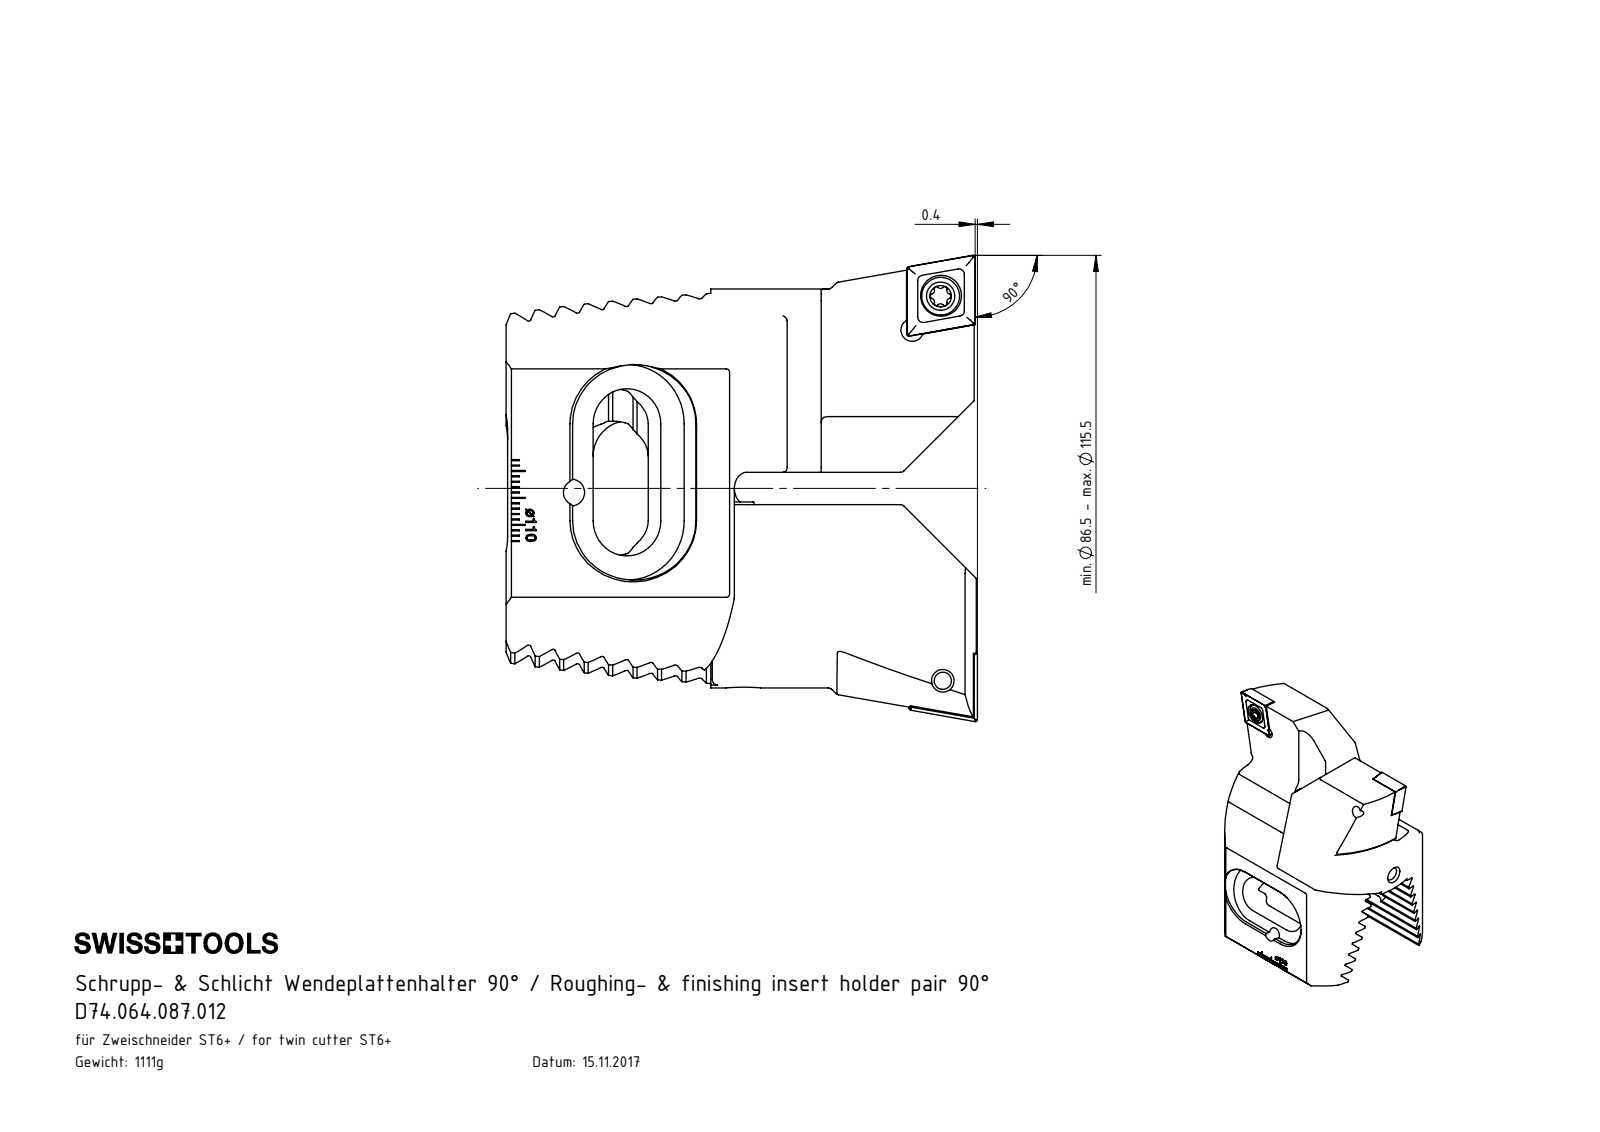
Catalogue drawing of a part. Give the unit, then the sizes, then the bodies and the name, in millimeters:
Units: millimetres
Overall size (bounding box): 87.5 × 86.5 × 58.2
Round holes (diameter × count): ⌀4.2 ×4, ⌀5 ×2, ⌀5.5 ×2, ⌀7.6 ×2, ⌀2 ×1, ⌀2.5 ×1, ⌀8 ×1
Round bosses / shafts (diameter × count): ⌀7 ×2, ⌀5 ×2, ⌀6 ×1, ⌀4 ×1, ⌀3 ×1, ⌀2 ×1
Partial cylindrical surfaces — rounded edges, fillets, slot ends (radius × count): R0.34 ×16, R1 ×16, R0.39 ×12, R0.69 ×6, R0.69 ×6, R3 ×4, R6.5 ×4, R11 ×4
Main face-to-face distances: 4.07, 8.14, 20.36, 12.21, 28.8, 29.4, 58.2, 16.29, 20.34, 24.43
Hole centre spacings: 8.21, 8.33, 71.43, 20, 58.76, 65.23, 65.3, 65.33
Volume: 142 276 mm³ · Surface area: 37 228 mm²
Bodies: 8 solids, 746 faces (411 planar, 143 cylindrical, 192 other)
Part name (STEP PRODUCT): ISO 4028 - M3 x 5_M3x8; Z72-ER3.001.030; ZC7-xxx.001.050_A; ZC7-xxx.001.050_A_versetzt Combi (+3 more)
STEP written by: SolidWorks 2017 (CONFIG_CONTROL_DESIGN)
